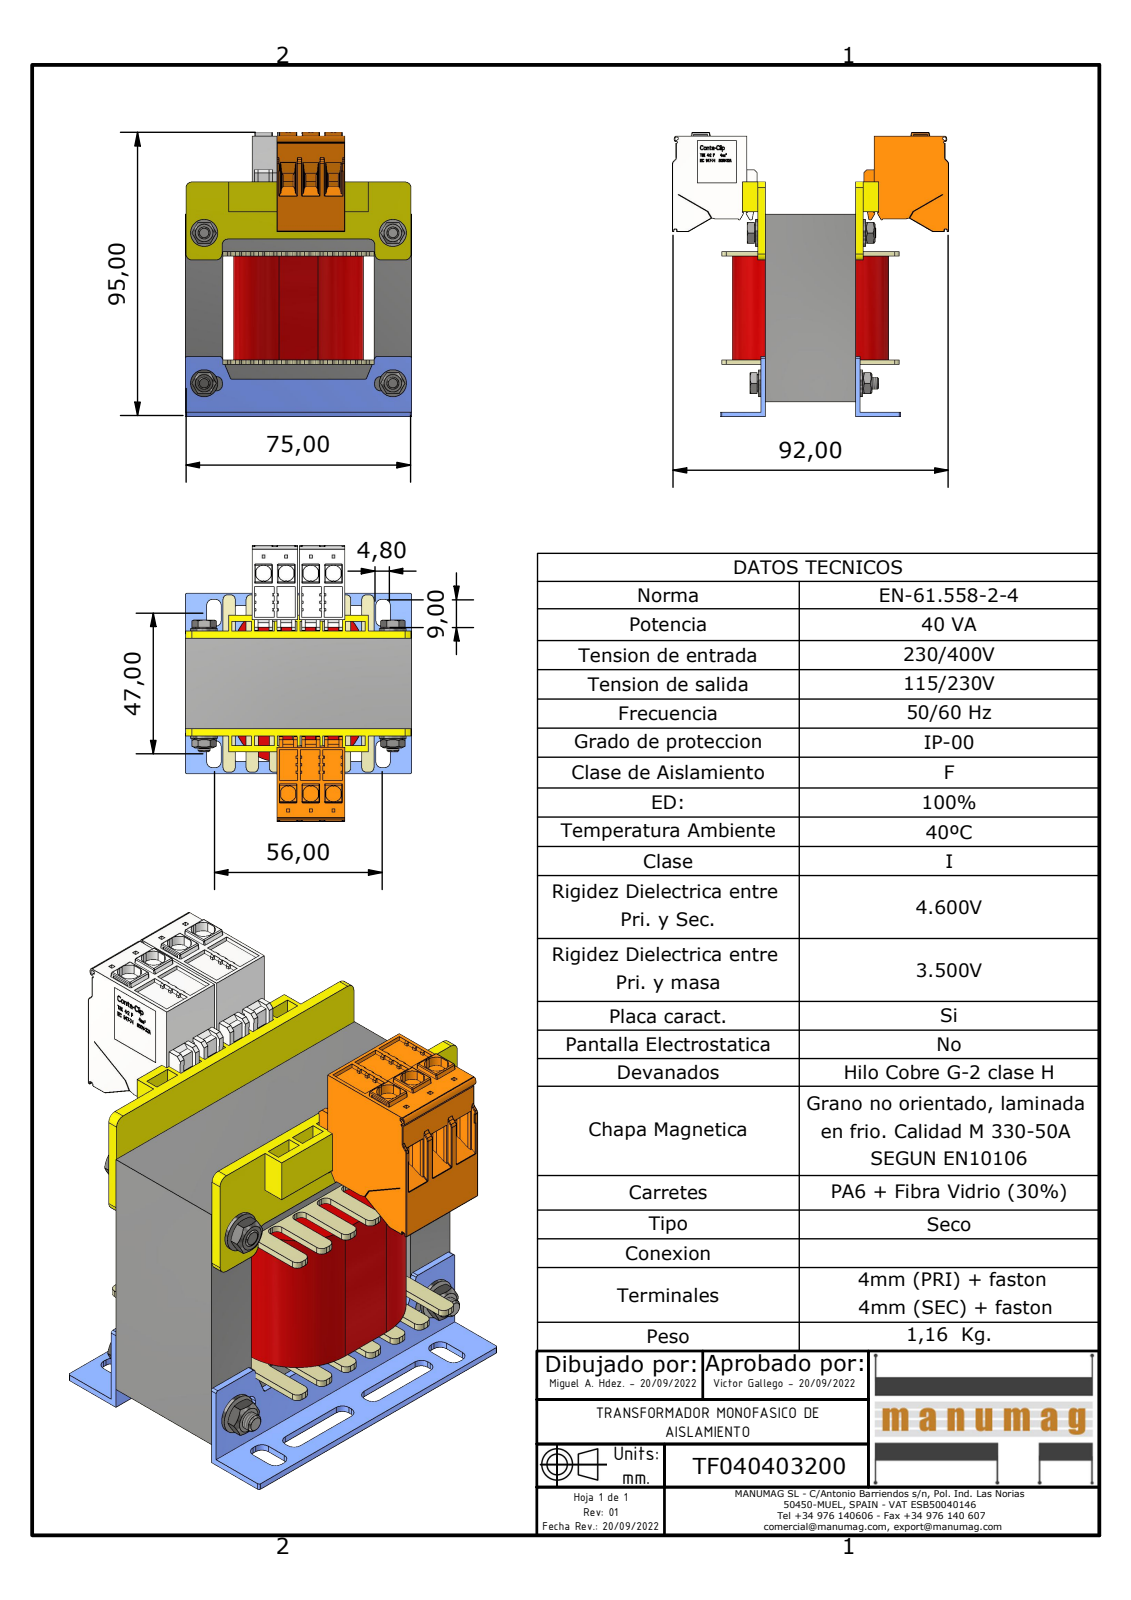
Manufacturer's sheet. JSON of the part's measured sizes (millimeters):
{"part_name": "TF040403200; EI75 x 62,5 - 30 (RC25); AF25DIN; EI 75 X 62,5 - 30 (+6 more)", "step_written_by": "Autodesk Inventor 2023 (AUTOMOTIVE_DESIGN)", "units": "millimeters", "bodies": {"solids": 25, "faces": 5918, "planar": 4734, "cylindrical": 821, "other": 363}, "overall_size": [94.65, 91.9, 75], "volume_mm3": 207147, "surface_area_mm2": 84070, "round_holes": [[3.24, 4], [4.3, 4], [4.5, 4], [4, 2]], "round_bosses_or_shafts": [[9, 4], [5.9, 4], [3.62, 4], [4, 2]], "partial_cylinders_radius": [[0.15, 259], [0.2, 81], [1.5, 52], [2, 48], [0.5, 32], [0.3, 12], [1, 8], [2.7, 7]], "face_to_face_distances": [12.5, 50, 30, 25, 1.5, 37.5, 62.5, 34, 2.5, 32.5], "hole_center_spacings": [50, 62.5, 80.04]}
